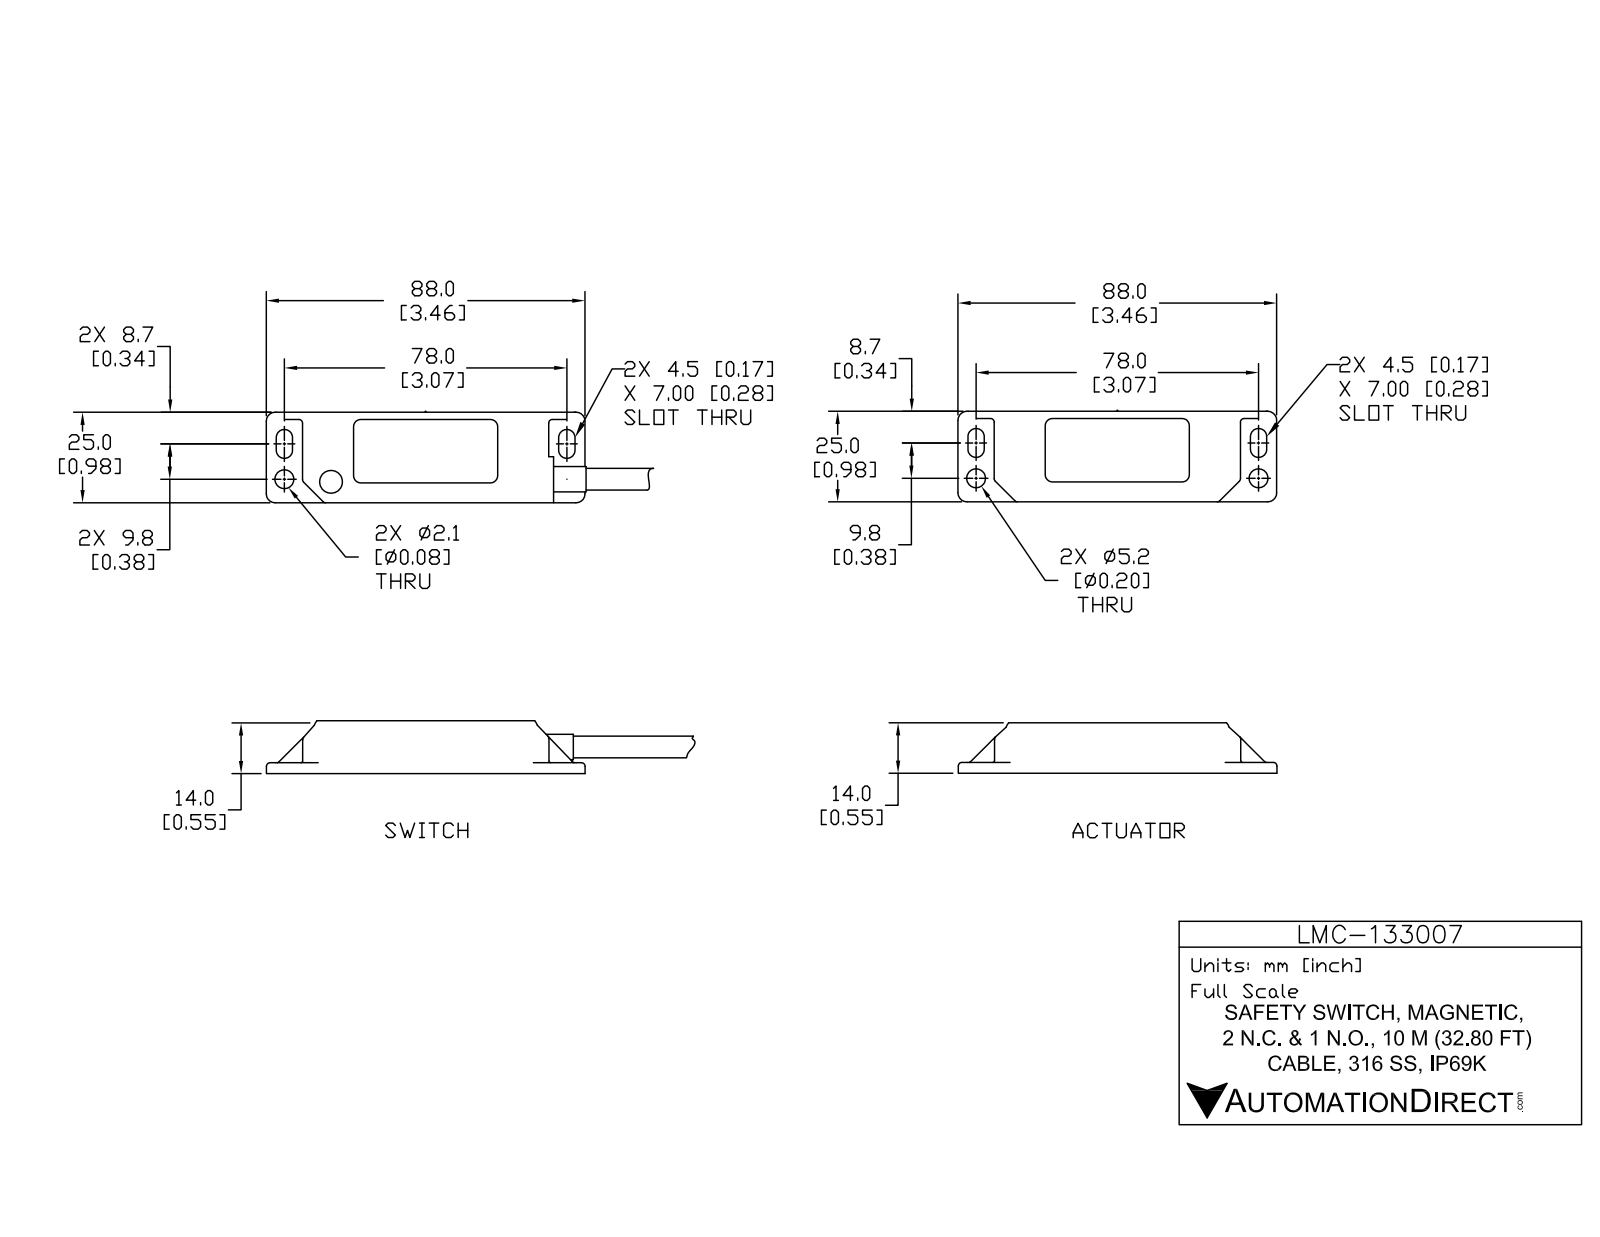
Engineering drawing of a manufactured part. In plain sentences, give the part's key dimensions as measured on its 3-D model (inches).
The part is named "LMC-133007_1; LMC-133007_2; LMC-133007". Its 3-D file was written by "SolidWorks 2017 (AUTOMOTIVE_DESIGN)". It is 10 solids with 676 faces: 194 planar, 244 cylindrical and 238 other. Overall it measures 9.186 by 2.008 by 0.551 inches. Its volume is 1.66 cubic inches and its surface area 46.34 square inches. Round holes: 4 of diameter 0.197, 4 of diameter 0.213, 1 of diameter 0.232, 1 of diameter 0.283. Round bosses or shafts: 4 of diameter 0.079, 2 of diameter 0.193, 2 of diameter 0.134, 1 of diameter 0.339, 1 of diameter 0.299, 1 of diameter 0.28, 1 of diameter 0.236. Partial cylindrical surfaces (rounded edges, fillets, slot ends): 95 of radius 0.02, 45 of radius 0.039, 8 of radius 0.091, 4 of radius 0.098, 4 of radius 0.256, 1 of radius 0.193. The main face-to-face distances are 0.067, 0.055, 0.543, 1.024, 0.476, 0.488, 0.421, 0.917, 0.106, 0.039. The hole center spacings are 0.67, 1.172, 1.181, 1.243, 1.496, 1.687, 1.815, 1.907.
